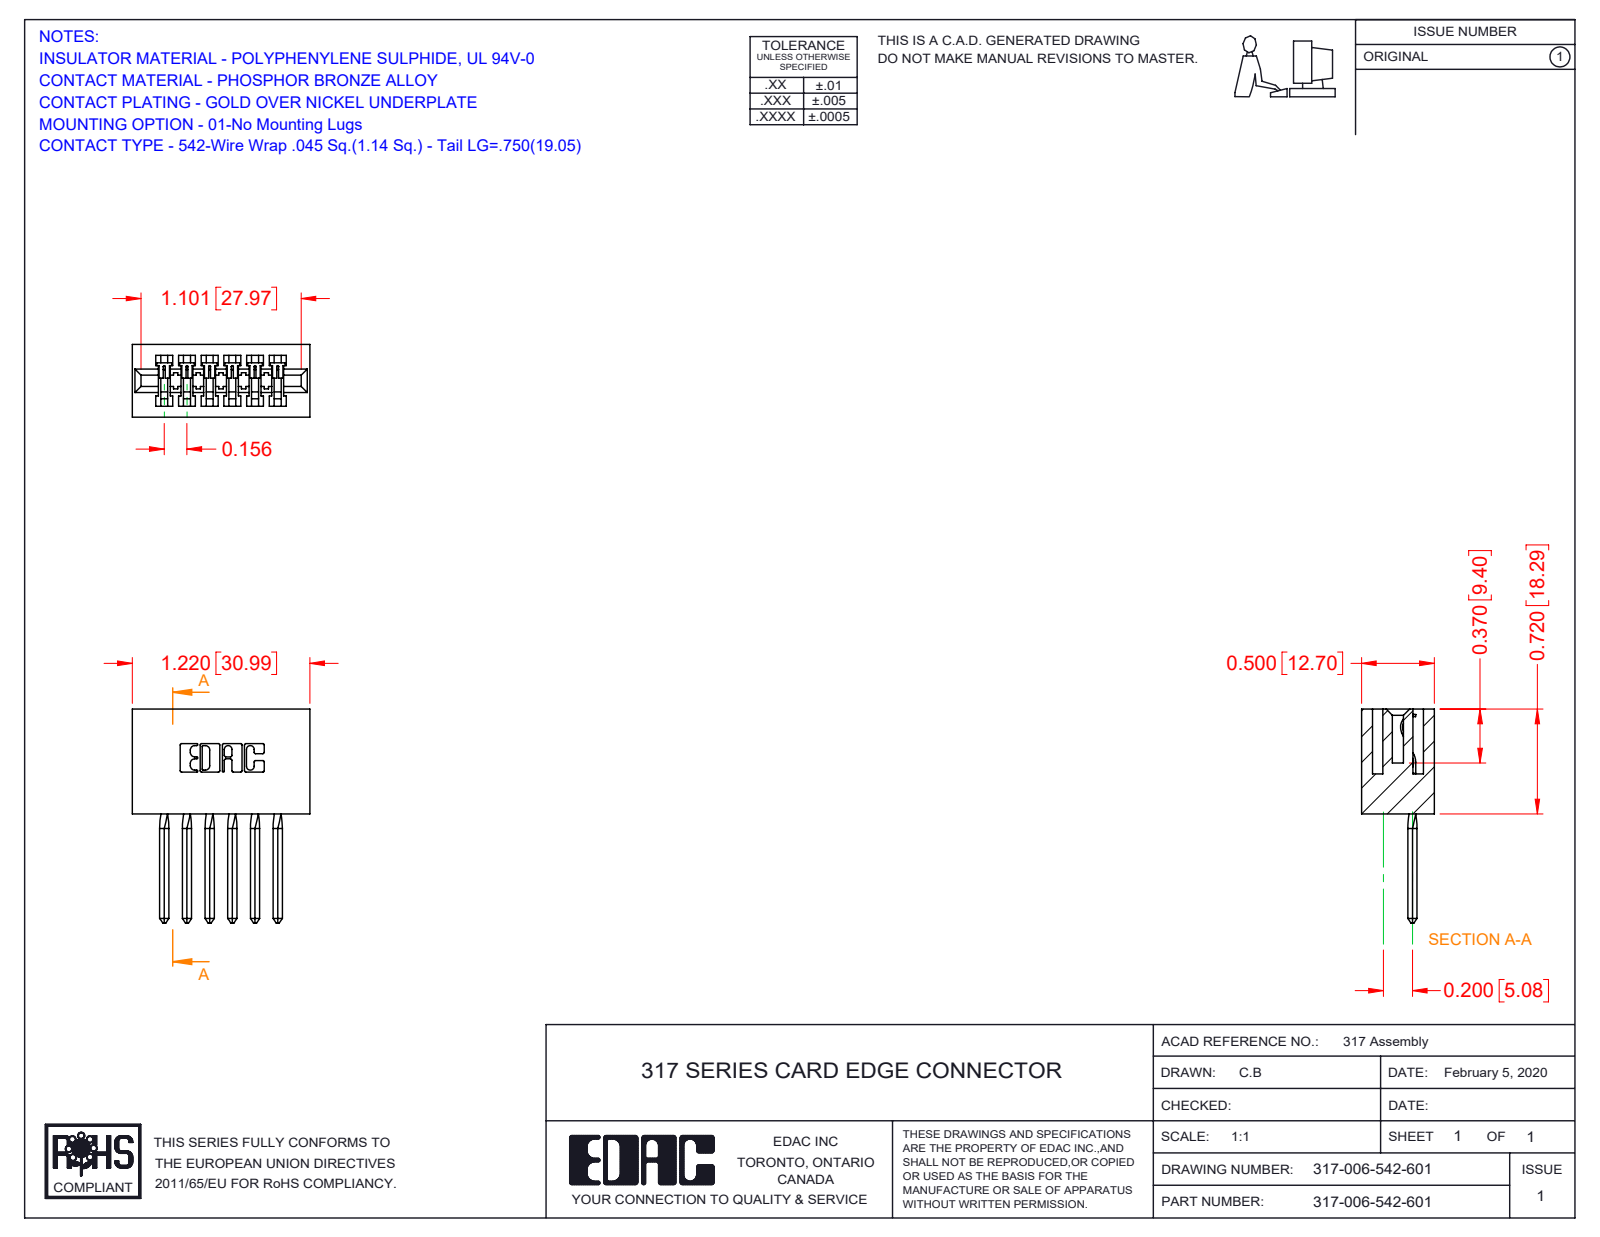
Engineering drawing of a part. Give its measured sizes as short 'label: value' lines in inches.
name: 317-006-542-601; 317-290-003_542; 317 Part_Lugless
written by: SolidWorks 2016 (CONFIG_CONTROL_DESIGN)
unit: in
bodies: 7 solids, 540 faces (434 planar, 82 cylindrical, 24 other)
size: 1.47 × 1.22 × 0.5
volume: 0.331 in³; area: 9.054 in²
rounds: 22× R0.01, 12× R0.006, 6× R0.007, 6× R0.031, 3× R0.026, 1× R0.074, 1× R0.089, 1× R0.1
face distances: 0.5, 0.075, 0.425, 0.156, 0.11, 0.065, 0.116, 0.312, 0.136, 1.22
